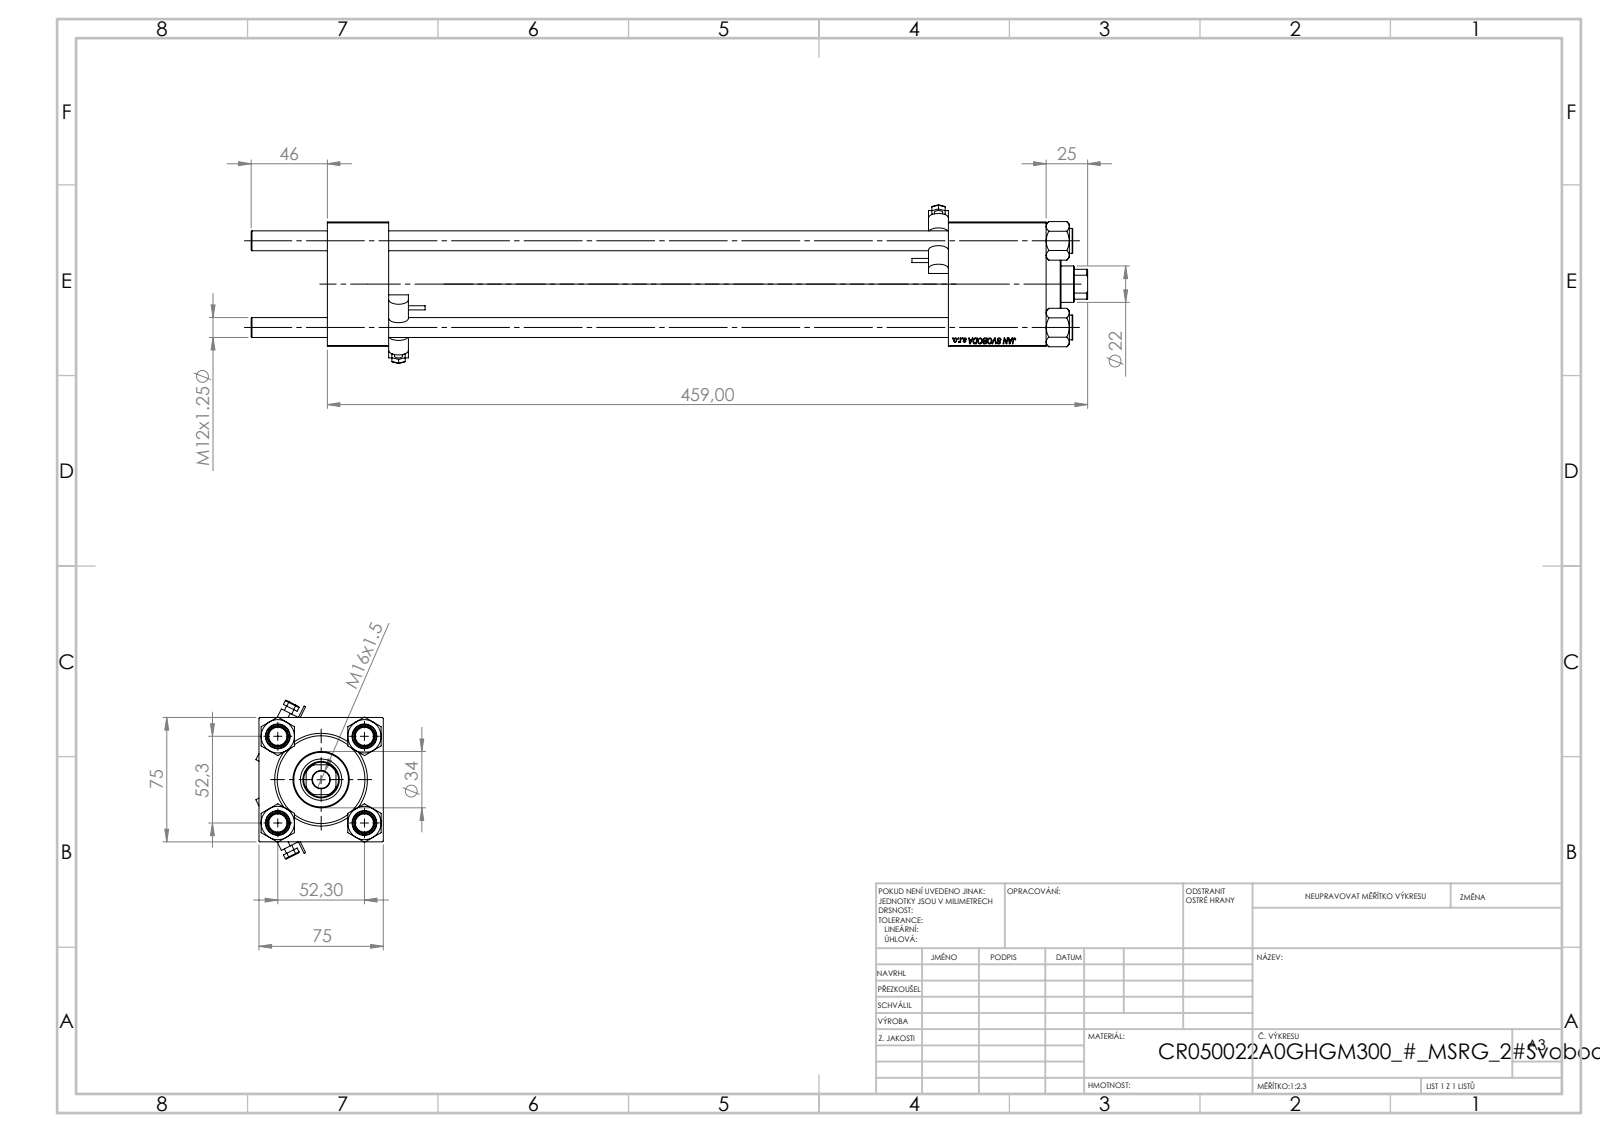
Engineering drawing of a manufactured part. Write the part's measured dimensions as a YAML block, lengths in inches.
part_name: "NUT_M5; CR025_012_A_0_G_A_G_M_020_+#_##_TYCINKA; V215CR_VCP; V215CR_BODY_A (+2 more)"
step_written_by: "SolidWorks 2019 (CONFIG_CONTROL_DESIGN)"
units: inches
bodies: {solids: 13, faces: 1198, planar: 556, cylindrical: 106, other: 536}
overall_size: [19.882, 3.772, 3.027]
volume: 65.3
surface_area: 500.7
round_holes:
  - {diameter: 0.472, count: 4}
  - {diameter: 0.276, count: 2}
  - {diameter: 0.825, count: 2}
  - {diameter: 1.181, count: 2}
  - {diameter: 0.413, count: 1}
  - {diameter: 0.866, count: 1}
  - {diameter: 0.984, count: 1}
  - {diameter: 1.614, count: 1}
  - {diameter: 1.969, count: 1}
  - {diameter: 2.087, count: 1}
round_bosses_or_shafts:
  - {diameter: 0.591, count: 4}
  - {diameter: 0.197, count: 2}
  - {diameter: 0.098, count: 2}
  - {diameter: 2.205, count: 1}
  - {diameter: 1.339, count: 1}
partial_cylinders:
  - {radius: 0.02, count: 12}
  - {radius: 0.236, count: 4}
  - {radius: 0.413, count: 1}
face_to_face_distances: [2.953, 1.457, 17.087, 15.63, 14.764, 13.307, 2.323, 15.957, 14.5, 1.193]
hole_center_spacings: [1.456, 2.059, 2.912, 14.705]
